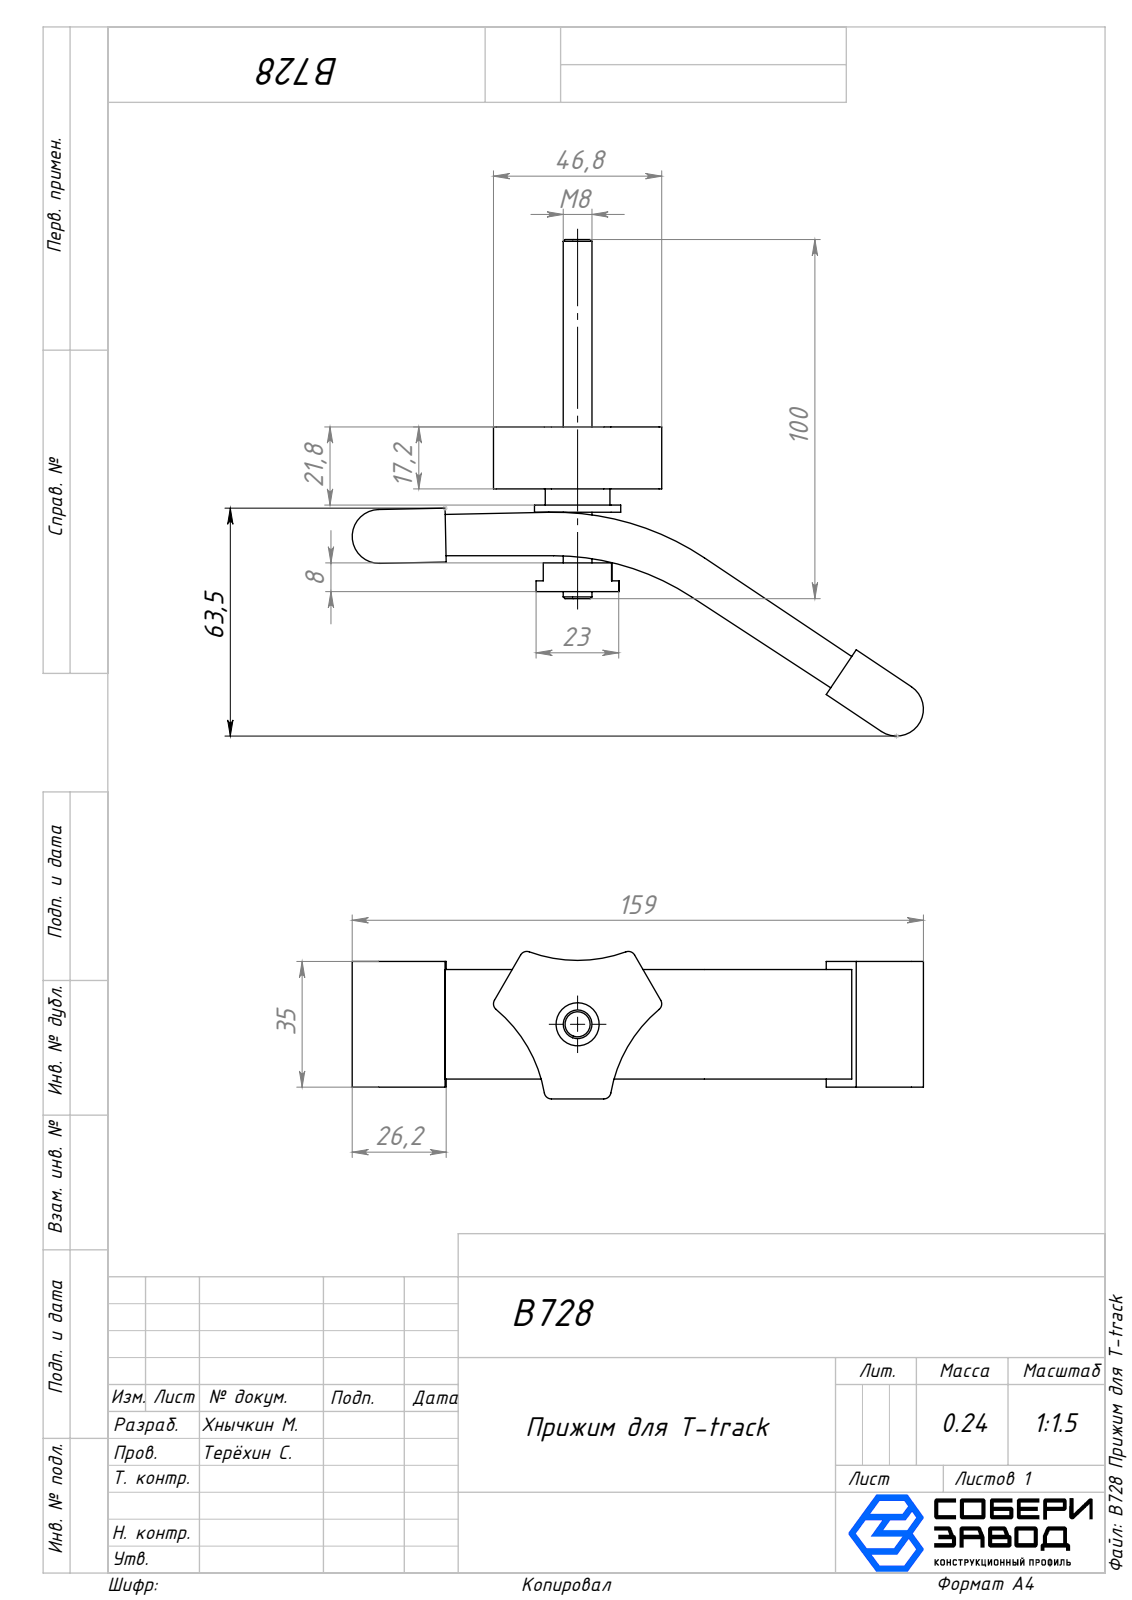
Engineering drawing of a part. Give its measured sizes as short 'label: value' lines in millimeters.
name: B728 Шайба_00; Вал М8х100_00; B728 Прижим для T-track; Сухарь М8_00 (+2 more)
written by: SolidWorks 2025 (AUTOMOTIVE_DESIGN)
unit: mm
bodies: 5 solids, 104 faces (52 planar, 40 cylindrical, 12 other)
size: 158.95 × 138.25 × 41.08
volume: 87 374 mm³; area: 31 215 mm²
holes: 1× ⌀6, 1× ⌀7, 1× ⌀8.5, 1× ⌀12
bosses: 1× ⌀24, 1× ⌀18, 1× ⌀8
rounds: 6× R2, 3× R39, 3× R41.5, 2× R4, 2× R7.5, 1× R70, 1× R75
face distances: 2.25, 32.75, 30.5, 2.5, 2, 14.11, 19.25, 35.86, 35, 8
